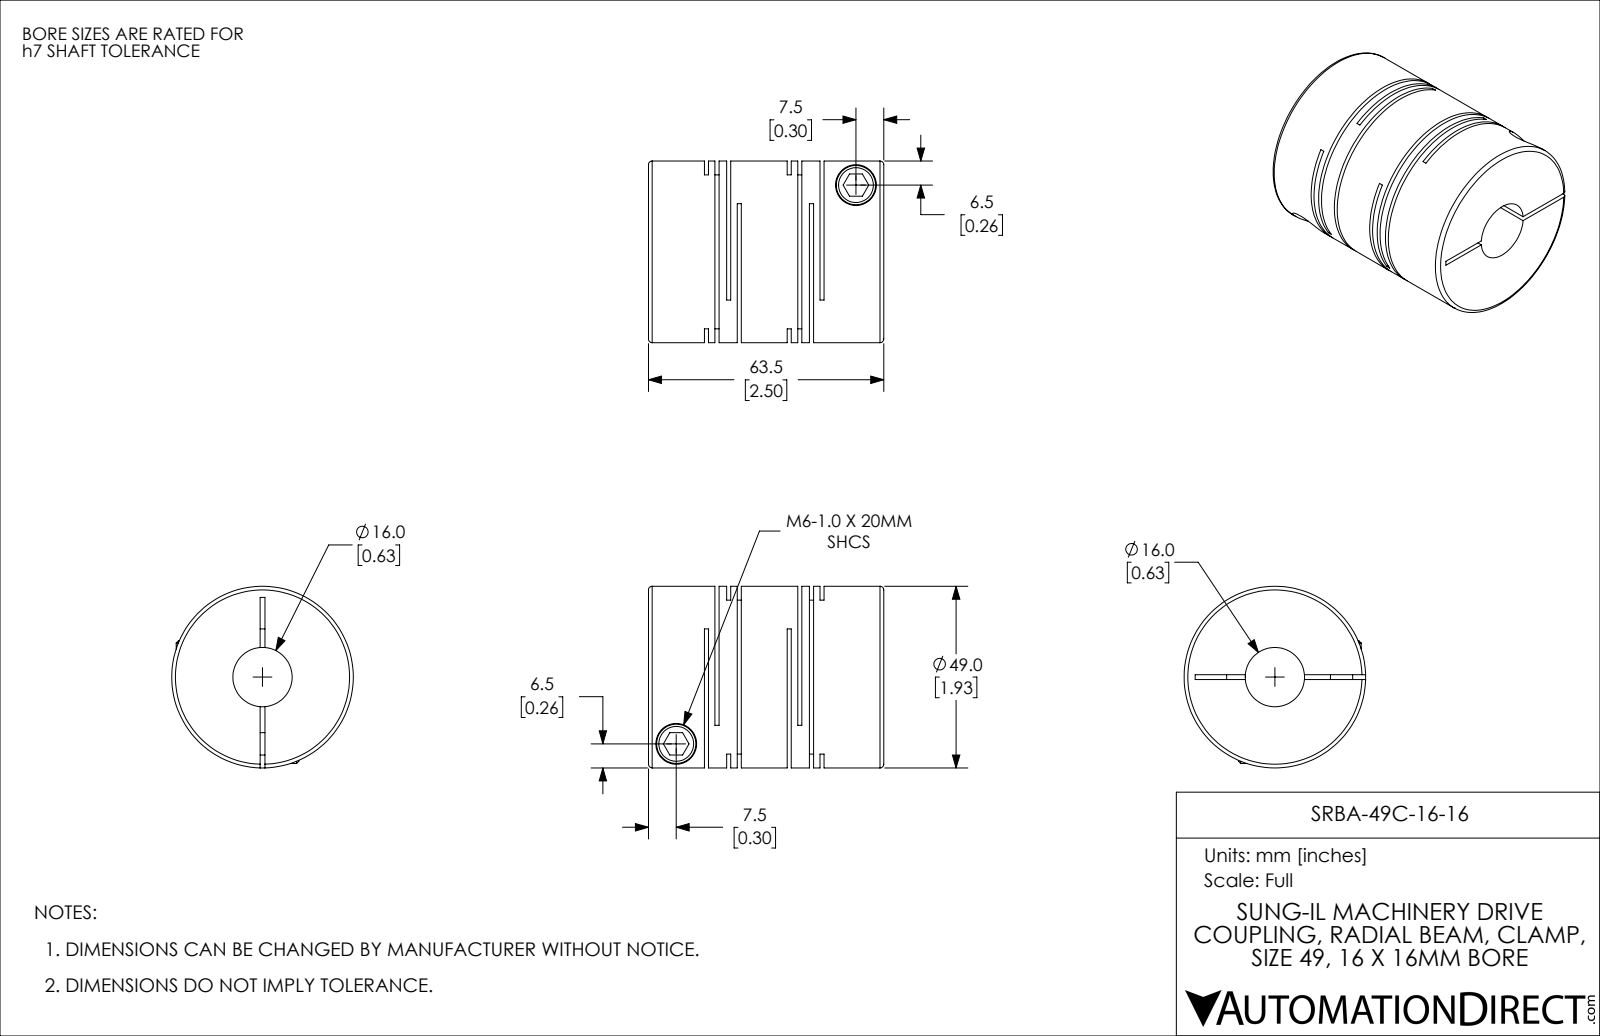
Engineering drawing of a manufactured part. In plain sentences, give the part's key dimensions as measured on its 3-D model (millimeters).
The part is named "SRBA-49C-16-16". Its 3-D file was written by "SolidWorks 2021 (CONFIG_CONTROL_DESIGN)". It is 1 solid with 114 faces: 60 planar, 42 cylindrical and 12 other. Overall it measures 63.5 by 49 by 49 millimeters. Its volume is 92 254 cubic millimeters and its surface area 39 546 square millimeters. Round holes: 2 of diameter 6, 2 of diameter 11, 1 of diameter 16. Round bosses or shafts: 2 of diameter 10.6, 1 of diameter 49. The main face-to-face distances are 6, 1.1, 2.85, 22.35, 1.75, 4.9, 21.25, 3.15, 19.5, 16.35.
